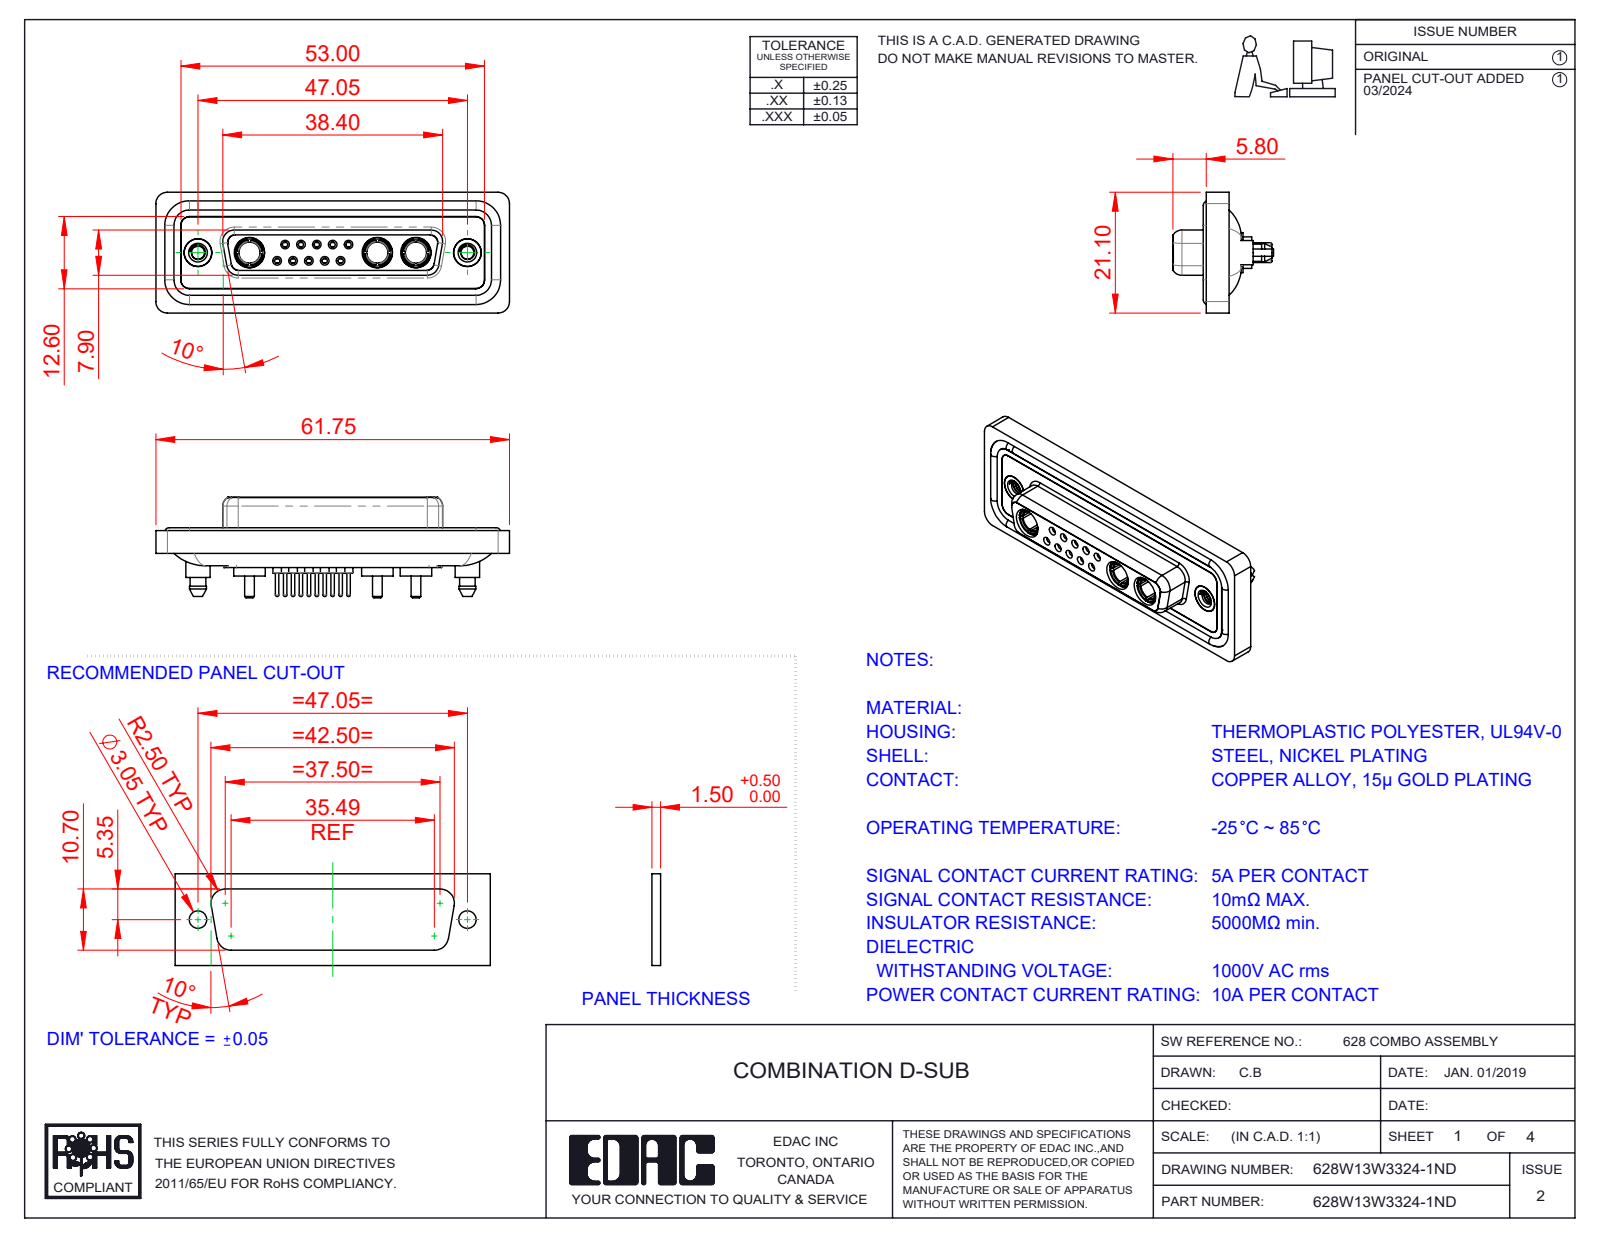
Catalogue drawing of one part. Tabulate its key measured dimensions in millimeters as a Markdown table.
| quantity | value |
| --- | --- |
| part name | Power Socket_10A S; 628W13W3324-1ND; 628Combo Housing_13W3; 628Combo Shell Rear_25 Contacts (+5 more) |
| STEP written by | SolidWorks 2023 (CONFIG_CONTROL_DESIGN) |
| units | millimeters |
| bodies | 23 solids, 1224 faces (358 planar, 495 cylindrical, 371 other) |
| overall size | 61.75 × 21.1 × 17.55 |
| volume | 8 365 mm³ |
| surface area | 14 010 mm² |
| round holes (diameter × count) | 0.9 × 10, 1.1 × 10, 1.5 × 10, 2 × 10, 1.6 × 5, 1.7 × 5, 4.85 × 5, 3.7 × 3, 5.3 × 3, 2.26 × 2, 4 × 2, 4.05 × 2 |
| round bosses / shafts (diameter × count) | 2.2 × 10, 0.6 × 10, 1.6 × 9, 5.5 × 3, 5.2 × 3, 4.96 × 3, 4.75 × 3, 3.75 × 3 |
| partial cylindrical surfaces (radius × count) | 1.5 × 24, 2 × 18, 1.6 × 10, 1.35 × 8, 0.25 × 4, 0.5 × 4, 0.6 × 4, 0.65 × 4 |
| main face-to-face distances | 0.4, 1.8, 7.45, 5.65, 0.5, 6.6, 7.05, 1.6, 2.9, 1.1 |
| hole center spacings | 3.16, 2.77, 5.03, 5.04, 5.54, 8.31, 7.49, 2.76 |
